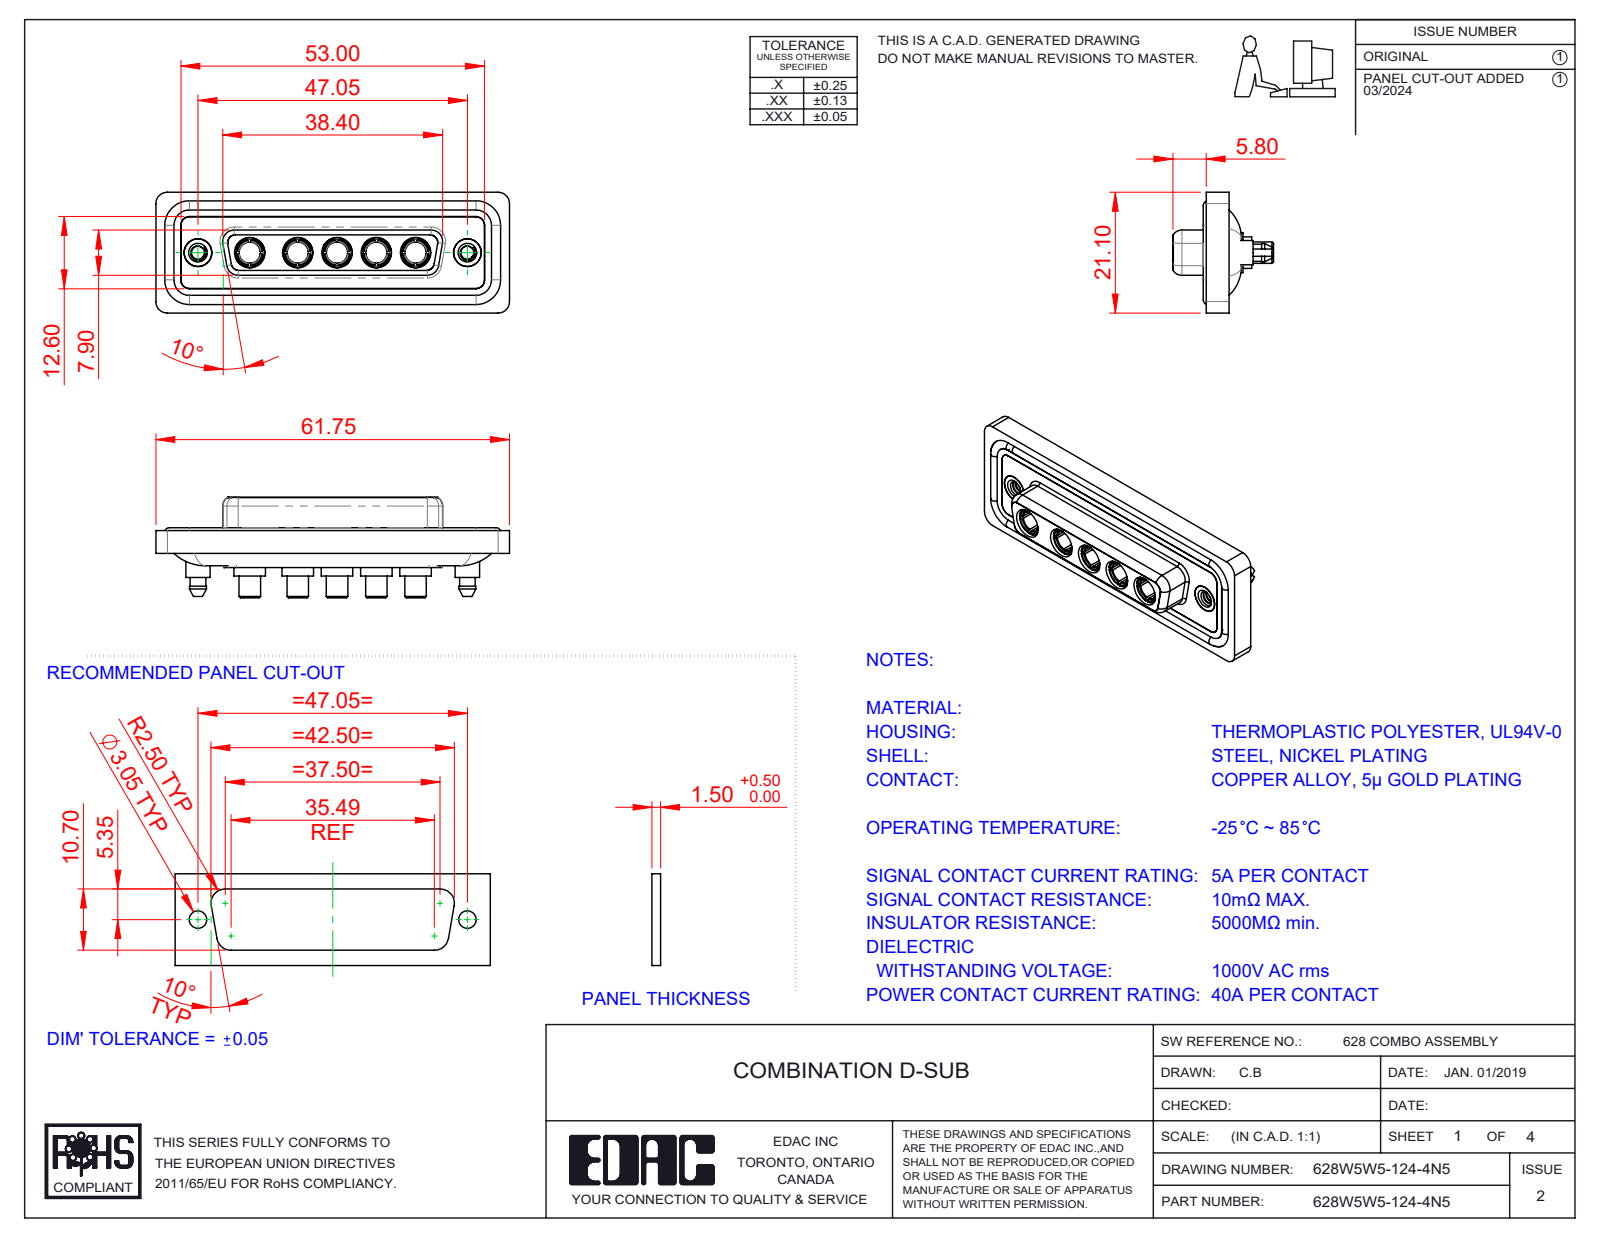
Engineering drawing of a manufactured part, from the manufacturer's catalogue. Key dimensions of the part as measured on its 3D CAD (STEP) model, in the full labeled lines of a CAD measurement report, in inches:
Part name (STEP PRODUCT): 628Combo Shell Front_25 Contacts; 628Combo Shell Rear_25 Contacts; 628Combo Housing_5W5; Power Socket_40A S (+3 more)
STEP written by: SolidWorks 2023 (CONFIG_CONTROL_DESIGN)
Units: inches
Bodies: 17 solids, 806 faces (266 planar, 335 cylindrical, 205 other)
Overall size (bounding box): 2.431 × 0.831 × 0.691
Volume: 0.513 in³ · Surface area: 21.39 in²
Round holes (diameter × count): ⌀0.191 ×7, ⌀0.146 ×5, ⌀0.209 ×5, ⌀0.089 ×2, ⌀0.157 ×2, ⌀0.159 ×2, ⌀0.197 ×2
Round bosses / shafts (diameter × count): ⌀0.217 ×5, ⌀0.205 ×5, ⌀0.195 ×5, ⌀0.187 ×5, ⌀0.148 ×5, ⌀0.063 ×4, ⌀0.213 ×2, ⌀0.195 ×2
Partial cylindrical surfaces — rounded edges, fillets, slot ends (radius × count): R0.059 ×24, R0.079 ×18, R0.063 ×10, R0.053 ×8, R0.083 ×5, R0.01 ×4, R0.02 ×4, R0.024 ×4
Main face-to-face distances: 0.016, 0.071, 0.293, 0.222, 0.02, 0.278, 0.26, 0.063, 0.043, 0.114
Hole centre spacings: 0.27, 0.356, 0.54, 1.496, 0.33, 0.6, 0.626, 0.686
